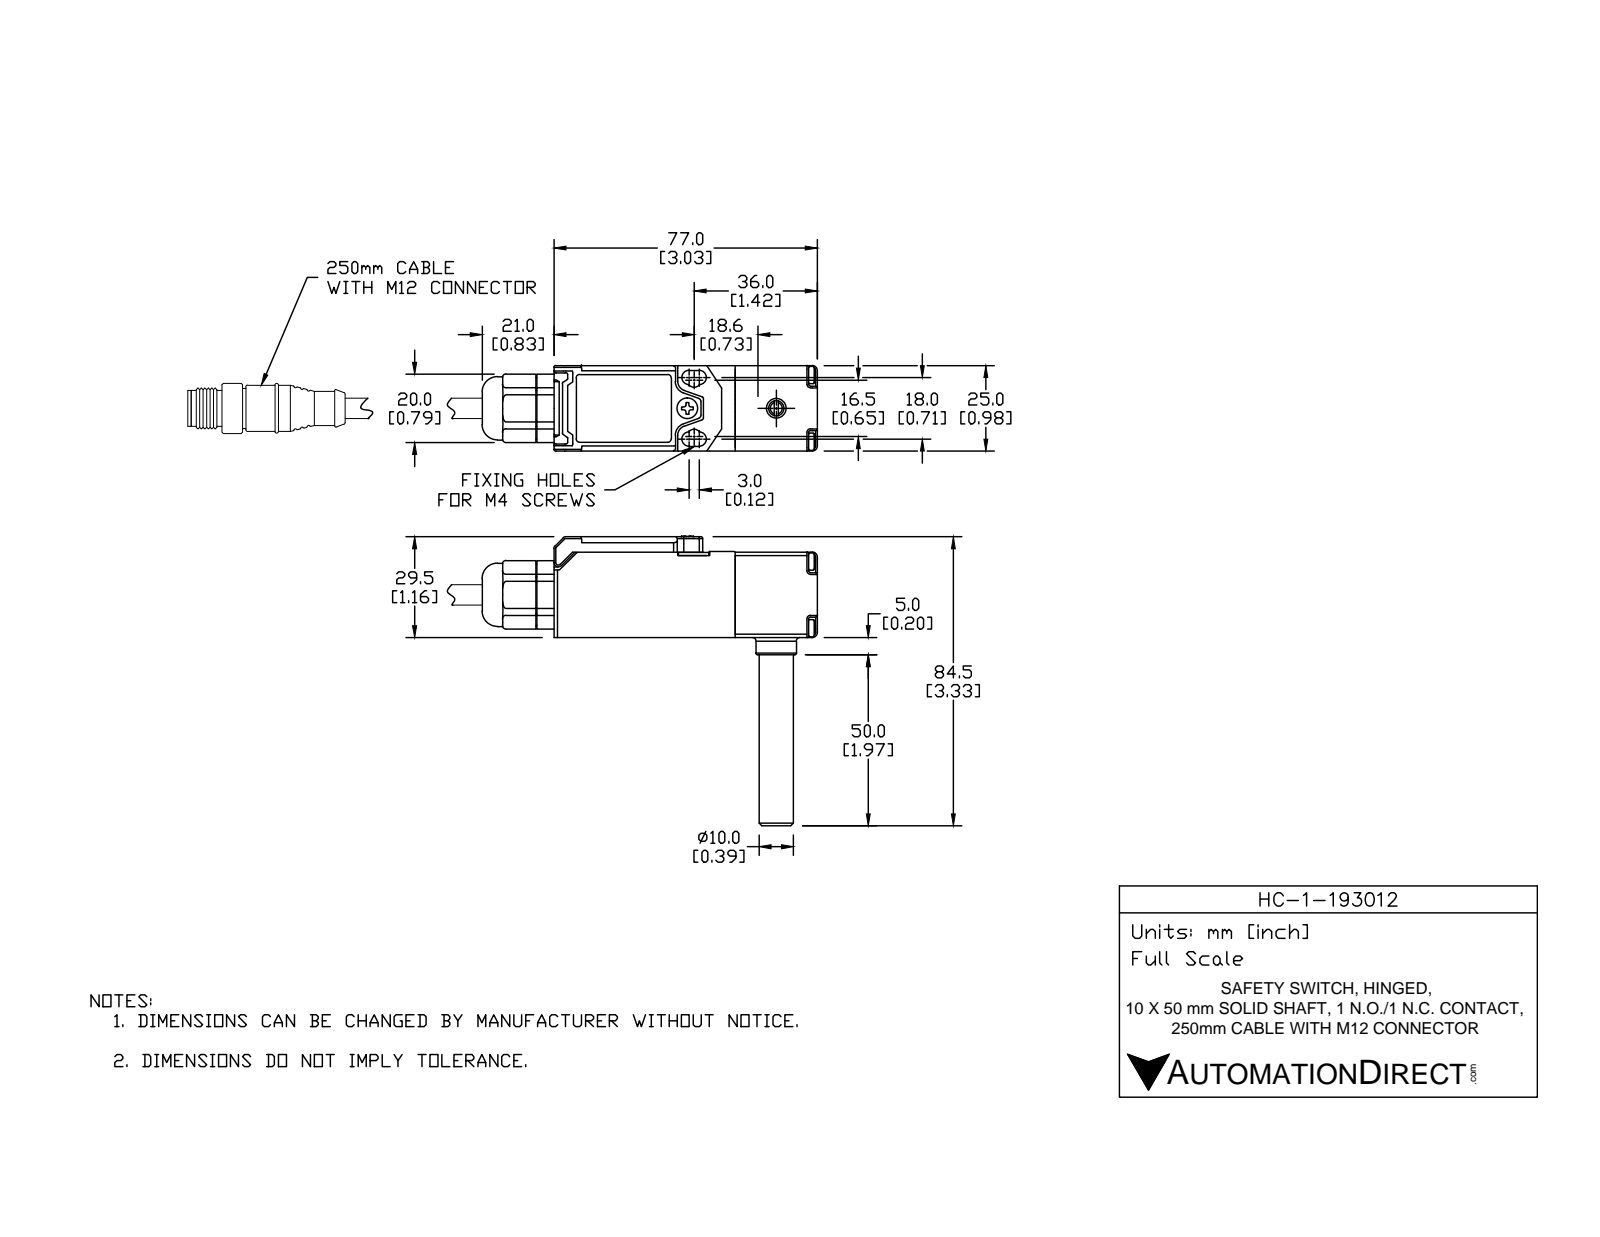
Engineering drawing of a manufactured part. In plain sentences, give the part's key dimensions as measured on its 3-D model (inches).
The part is named "HC-1-193012". Its 3-D file was written by "SolidWorks 2014 (AUTOMOTIVE_DESIGN)". It is 14 solids with 1702 faces: 700 planar, 601 cylindrical and 401 other. Overall it measures 3.336 by 3.169 by 0.984 inches. Its volume is 1.788 cubic inches and its surface area 43.04 square inches. Round holes: 5 of diameter 0.126, 4 of diameter 0.094, 2 of diameter 0.059, 2 of diameter 0.063, 2 of diameter 0.071, 2 of diameter 0.087, 2 of diameter 0.142, 1 of diameter 0.055, 1 of diameter 0.081, 1 of diameter 0.098, 1 of diameter 0.102, 1 of diameter 0.185. Round bosses or shafts: 5 of diameter 0.102, 4 of diameter 0.197, 4 of diameter 0.079, 2 of diameter 0.138, 1 of diameter 0.74, 1 of diameter 0.531, 1 of diameter 0.394, 1 of diameter 0.386. Partial cylindrical surfaces (rounded edges, fillets, slot ends): 226 of radius 0.02, 24 of radius 0.004, 20 of radius 0.012, 20 of radius 0.039, 7 of radius 0.059, 6 of radius 0.083, 6 of radius 0.11, 4 of radius 0.008. The main face-to-face distances are 0.984, 0.079, 0.071, 0.913, 0.039, 0.906, 0.945, 0.827, 0.874, 1.15. The hole center spacings are 0.543, 0.768, 0.171, 0.187, 0.245, 0.414, 0.423, 0.426.
